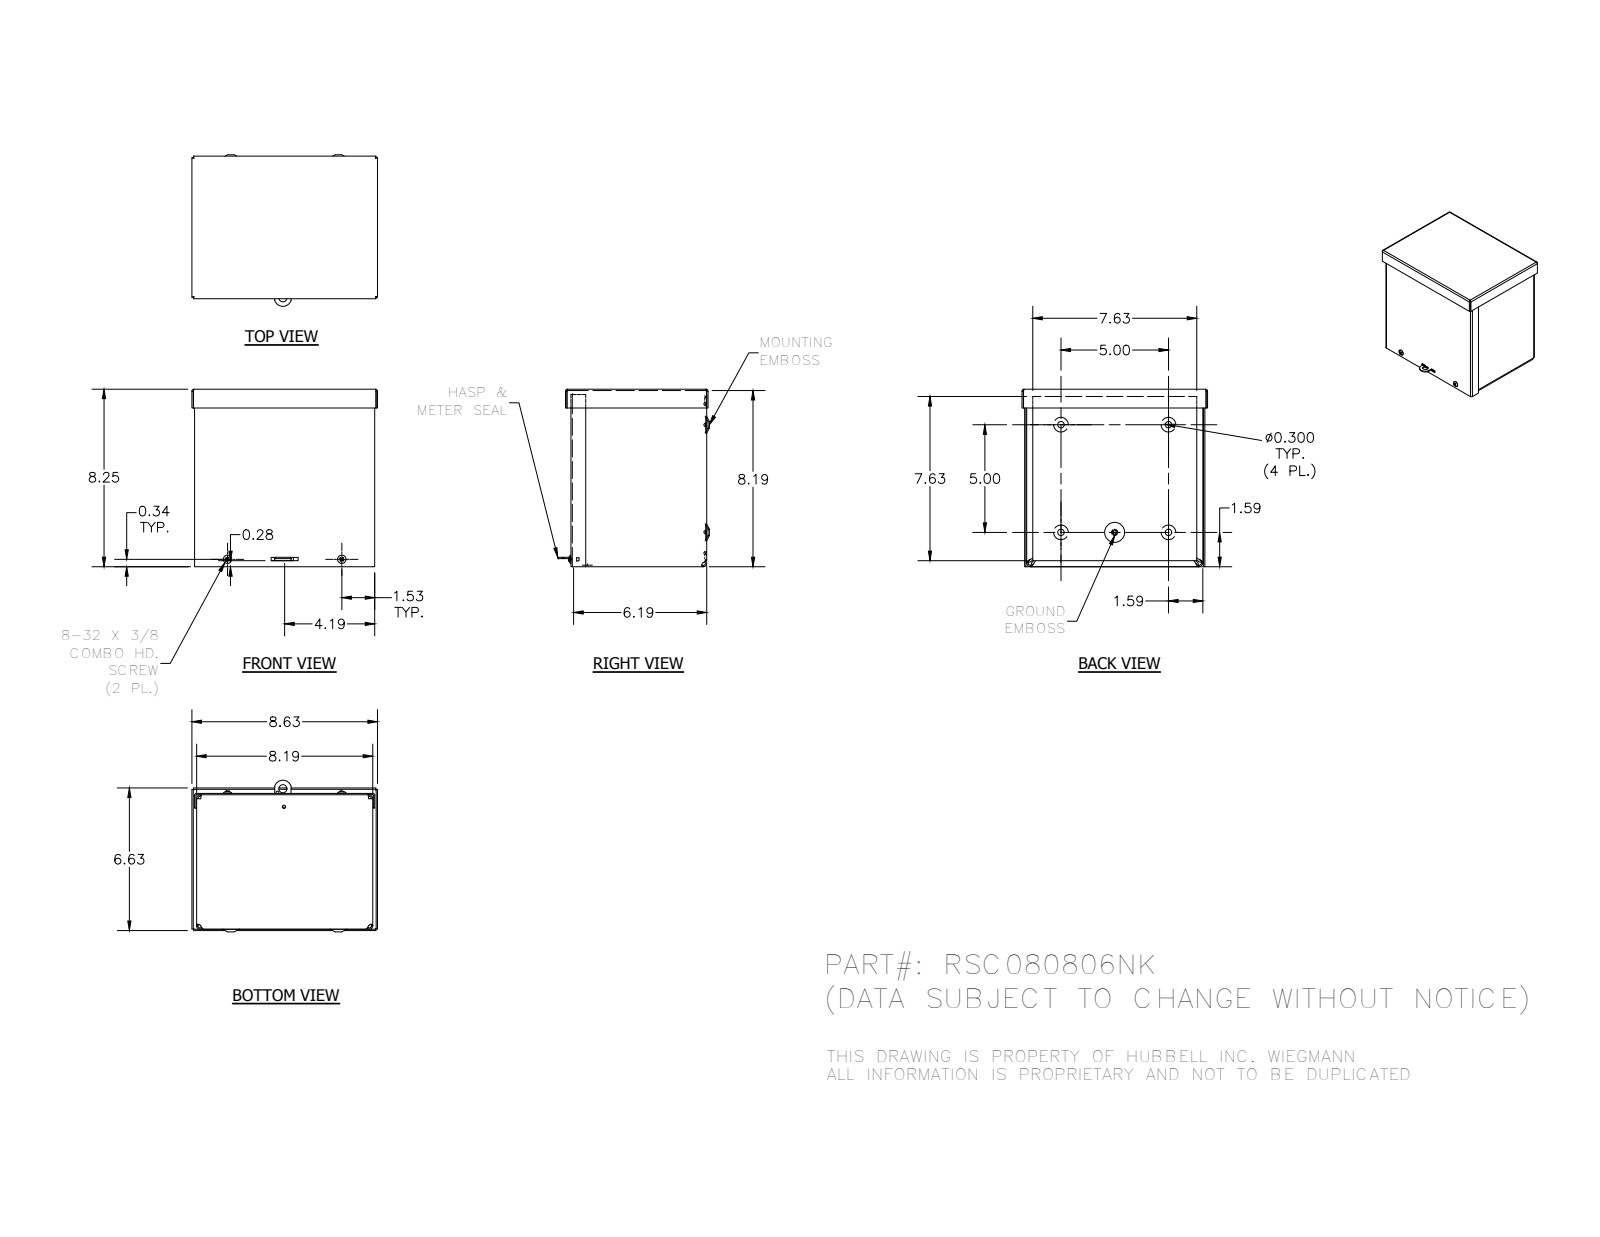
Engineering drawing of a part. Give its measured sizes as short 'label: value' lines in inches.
name: RSC080806NK_WRAP; RSC0808NK_LID; RSC0806NK_CAP; 3183 (+3 more)
written by: Autodesk Inventor 2014 (AUTOMOTIVE_DESIGN)
unit: in
bodies: 7 solids, 377 faces (163 planar, 78 cylindrical, 136 other)
size: 8.625 × 8.25 × 7.125
volume: 28.55 in³; area: 933.8 in²
holes: 4× ⌀0.3, 4× ⌀0.313, 2× ⌀0.148, 1× ⌀0.125, 1× ⌀0.136, 1× ⌀0.156, 1× ⌀0.165, 1× ⌀0.375
bosses: 2× ⌀0.384, 2× ⌀0.164, 1× ⌀0.228
rounds: 8× R0.031, 8× R0.093, 8× R0.125, 8× R0.187, 4× R0.055, 4× R0.062, 4× R0.094, 4× R0.117
face distances: 0.062, 8.126, 0.062, 8.188, 6.249, 0.124, 6.187, 0.063, 6.312, 6.25
hole spacings: 5, 1.072, 1.261, 2.5, 5.313, 5.59, 6.063, 6.253
